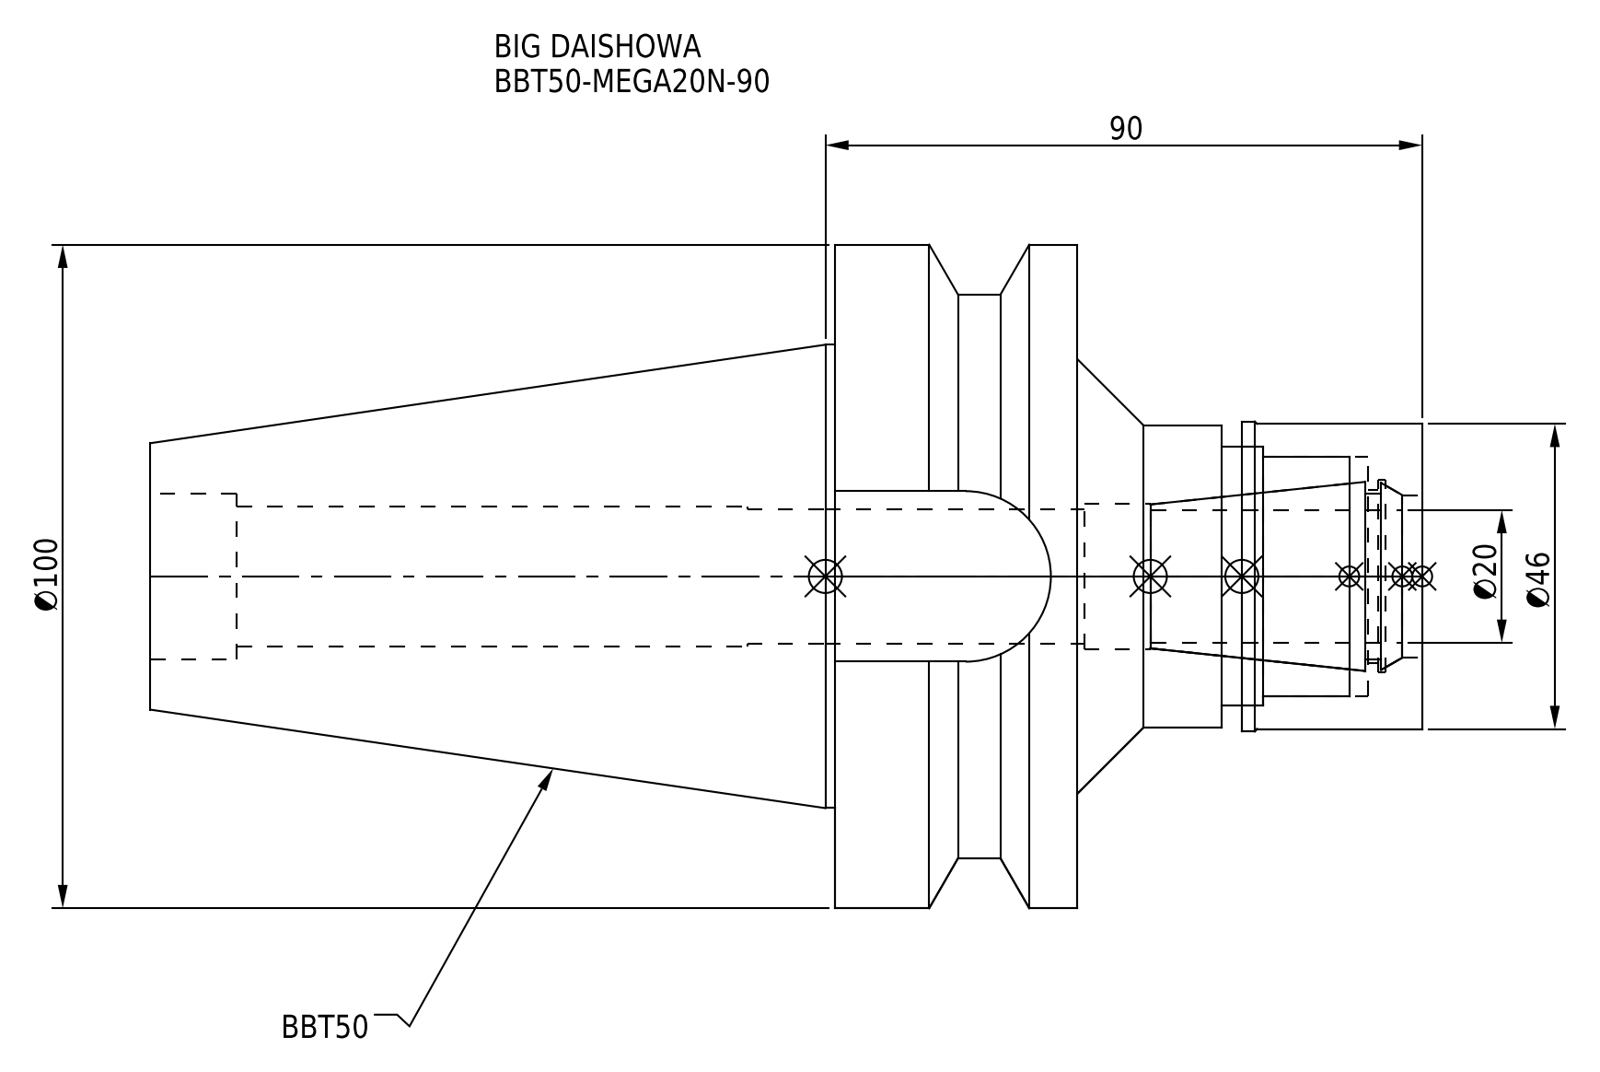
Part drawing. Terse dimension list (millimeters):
name: BBT50MN20090-200_ASM.stp; MGN20_1.stp; BBT50-MEGA20N-90_1.stp; DXF_TEMP_ASSY_ASM_4_ASM.stp (+3 more)
written by: SolidWorks 2019 (CONFIG_CONTROL_DESIGN)
unit: mm
bodies: 2 solids, 76 faces (22 planar, 40 cylindrical, 14 other)
size: 191.8 × 100 × 100
volume: 515 913 mm³; area: 70 963 mm²
holes: 1× ⌀20.3, 1× ⌀21.2, 1× ⌀22, 1× ⌀24.5, 1× ⌀25, 1× ⌀26, 1× ⌀29, 1× ⌀36, 1× ⌀39
bosses: 1× ⌀100, 1× ⌀85, 1× ⌀69.85, 1× ⌀46.7, 1× ⌀46, 1× ⌀45.5
rounds: 1× R12.85
face distances: 36.5, 52, 88.5, 191.8, 139.8, 103.3, 70.8, 27.2, 24.8, 61.3
